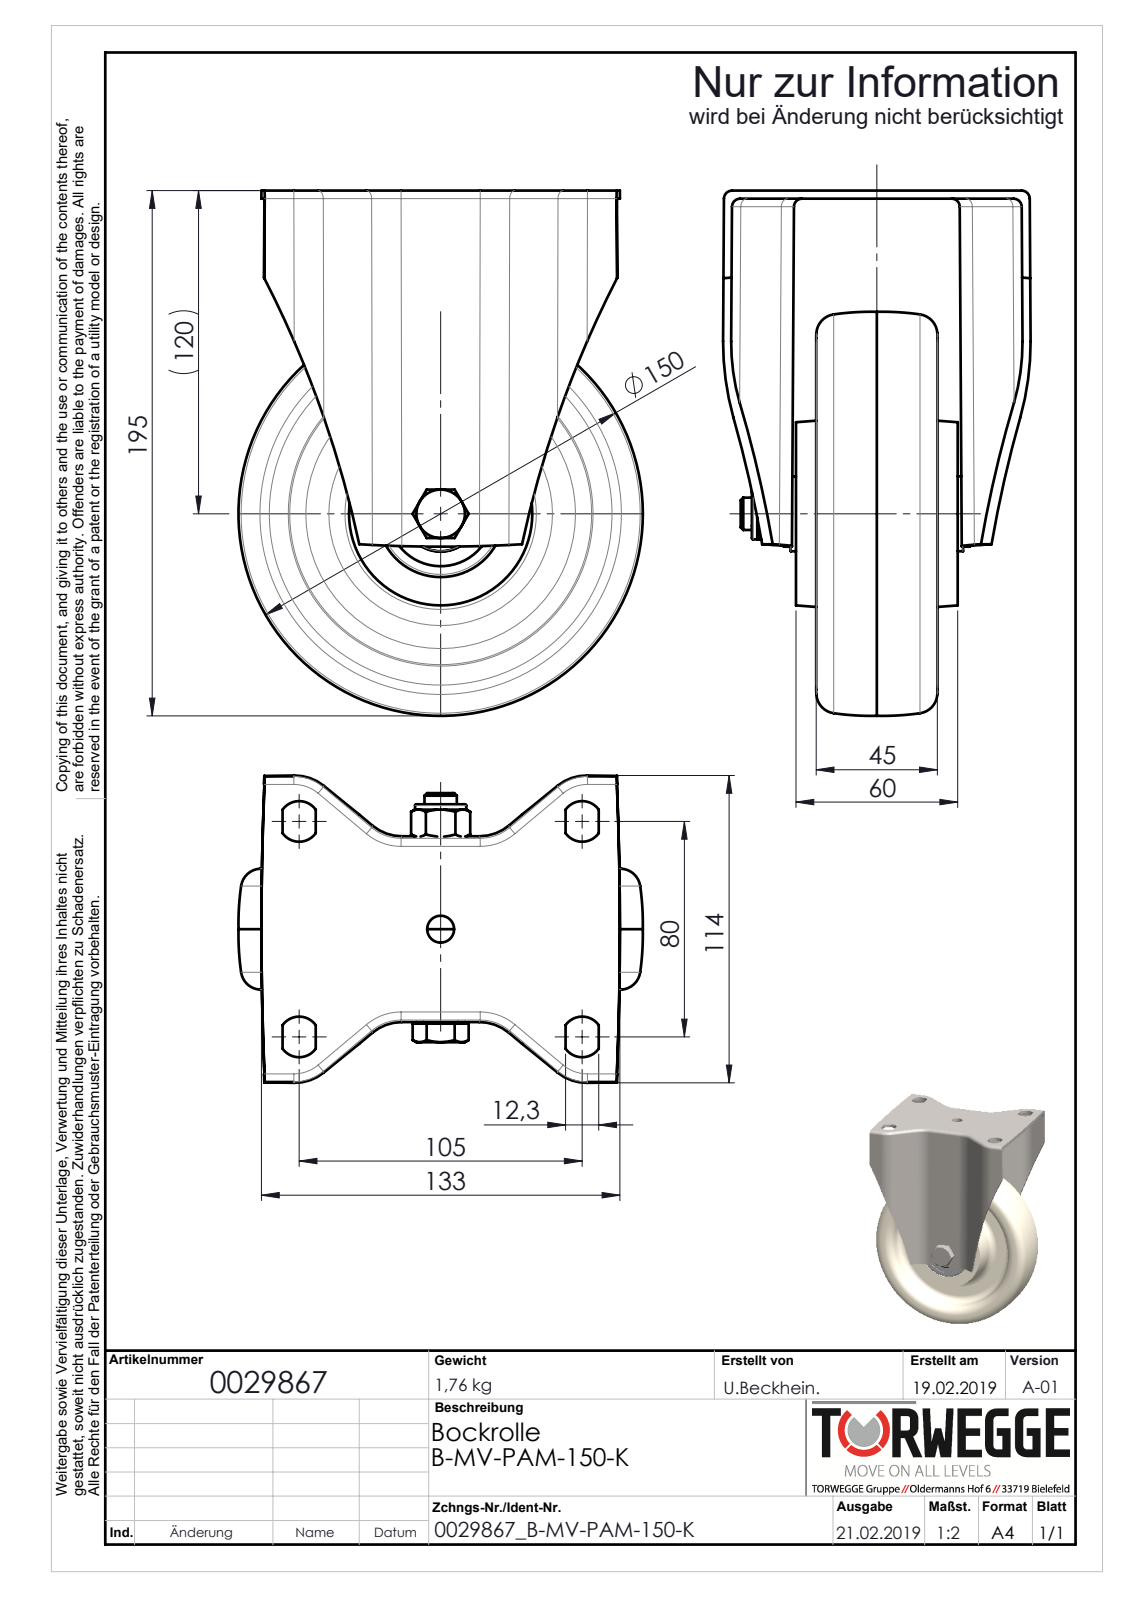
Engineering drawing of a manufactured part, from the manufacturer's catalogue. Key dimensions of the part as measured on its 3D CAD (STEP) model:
Part name (STEP PRODUCT): 0029867_B-MV-PAM-150-K_(A-01)
STEP written by: SolidWorks 2018 (AUTOMOTIVE_DESIGN)
Units: millimetres
Bodies: 0 solids, 345 faces (125 planar, 94 cylindrical, 126 other)
Overall size (bounding box): 195.02 × 150.04 × 114.1
Round holes (diameter × count): ⌀10 ×1, ⌀10.2 ×1, ⌀12.3 ×1, ⌀12.4 ×1, ⌀20 ×1, ⌀21 ×1, ⌀38.9 ×1
Round bosses / shafts (diameter × count): ⌀28.1 ×1, ⌀27.8 ×1, ⌀19.6 ×1, ⌀19 ×1, ⌀18 ×1, ⌀12 ×1
Partial cylindrical surfaces — rounded edges, fillets, slot ends (radius × count): R3 ×16, R17 ×8, R7.55 ×4, R14 ×4, R20 ×4, R400 ×2, R501.25 ×1
Main face-to-face distances: 3, 25, 35, 23, 60, 10, 20, 26, 0.5, 59.5
